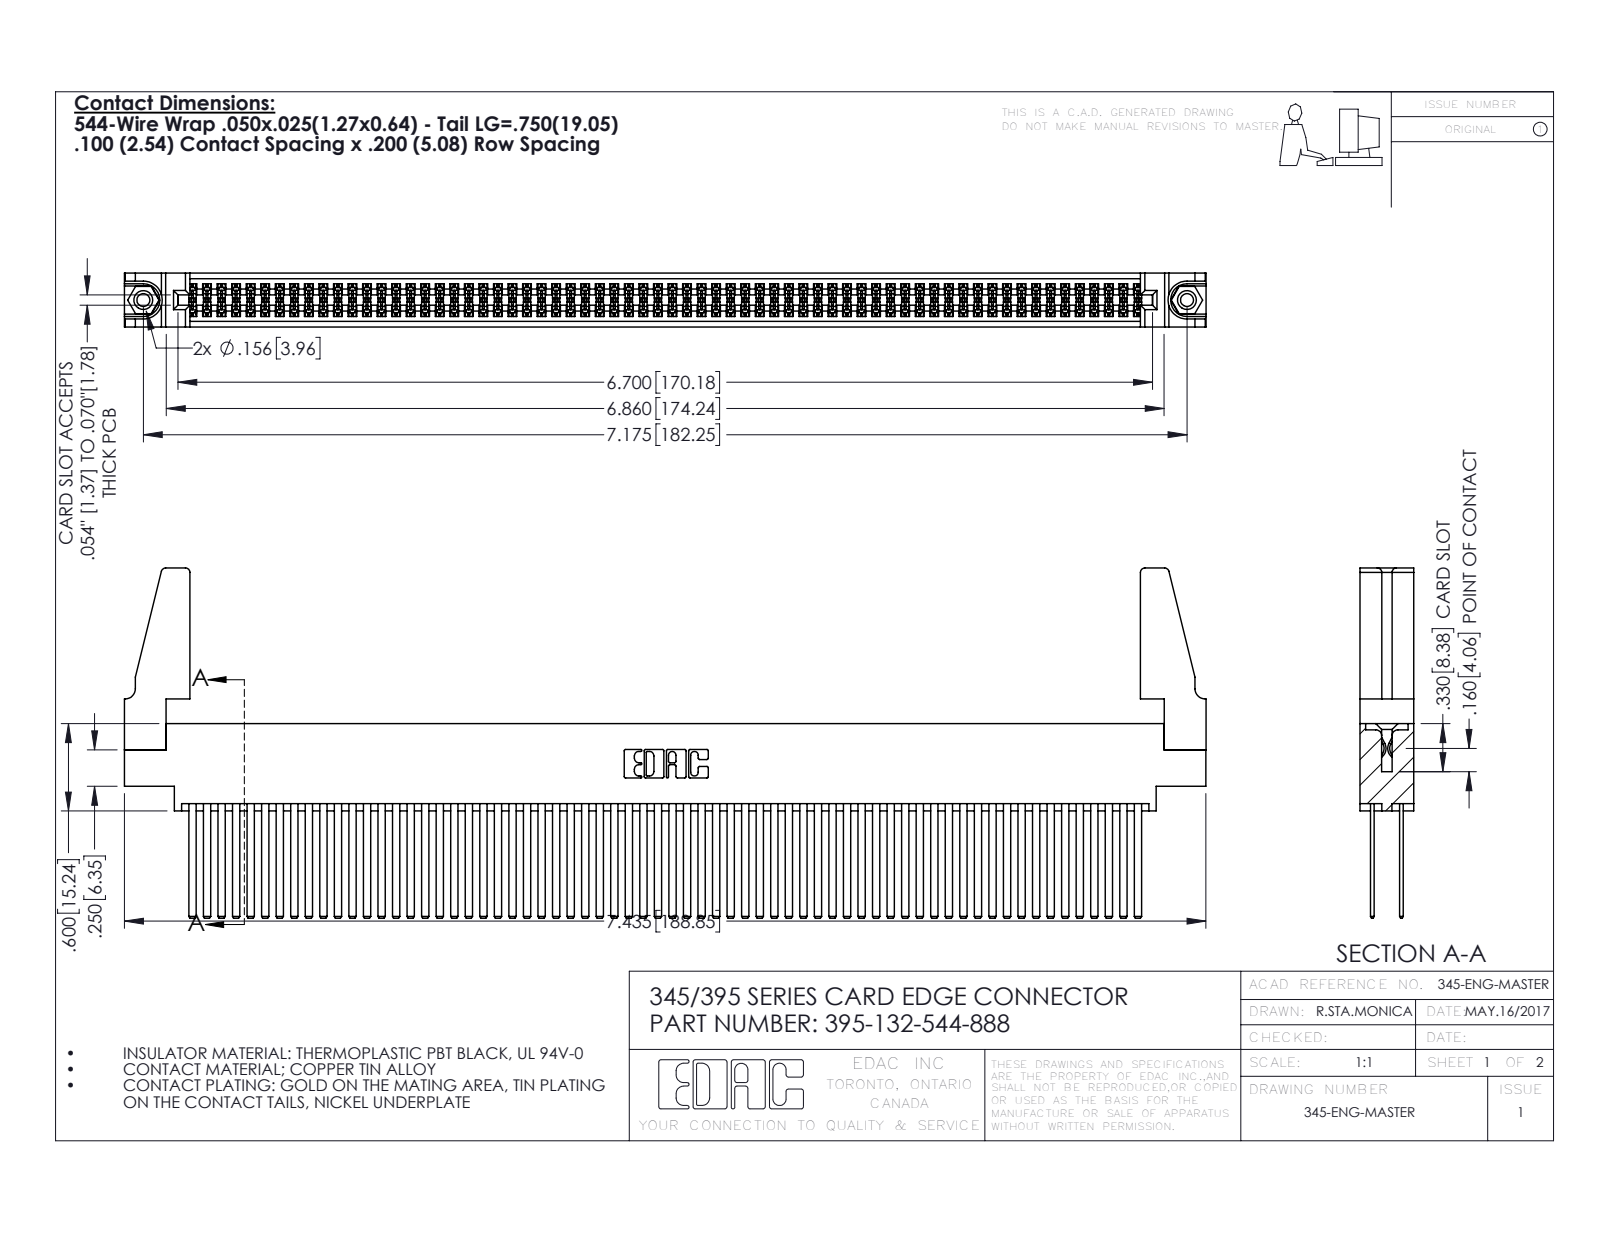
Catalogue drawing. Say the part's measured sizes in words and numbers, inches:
The part is named "395-132-544-888; 345-220-078_345-220-088; 345-292-001_345-293-144; 345-250-001_345-250-001-102 (+1 more)". Its 3-D file was written by "SolidWorks 2016 (CONFIG_CONTROL_DESIGN)". It is 137 solids with 6062 faces: 3984 planar, 2062 cylindrical and 16 other. Overall it measures 7.436 by 2.407 by 0.37 inches. Its volume is 1.438 cubic inches and its surface area 60.72 square inches. Round holes: 2 of diameter 0.089, 2 of diameter 0.125, 2 of diameter 0.156, 1 of diameter 0.064. Round bosses or shafts: 2 of diameter 0.155. Partial cylindrical surfaces (rounded edges, fillets, slot ends): 198 of radius 0.006, 22 of radius 0.01, 8 of radius 0.03, 6 of radius 0.007, 6 of radius 0.031, 3 of radius 0.026, 2 of radius 0.014, 2 of radius 0.019. The main face-to-face distances are 0.072, 0.298, 0.2, 0.098, 0.272, 0.025, 0.225, 0.37, 0.175, 0.149. The hole center spacings are 0.27, 6.939, 7.175.
